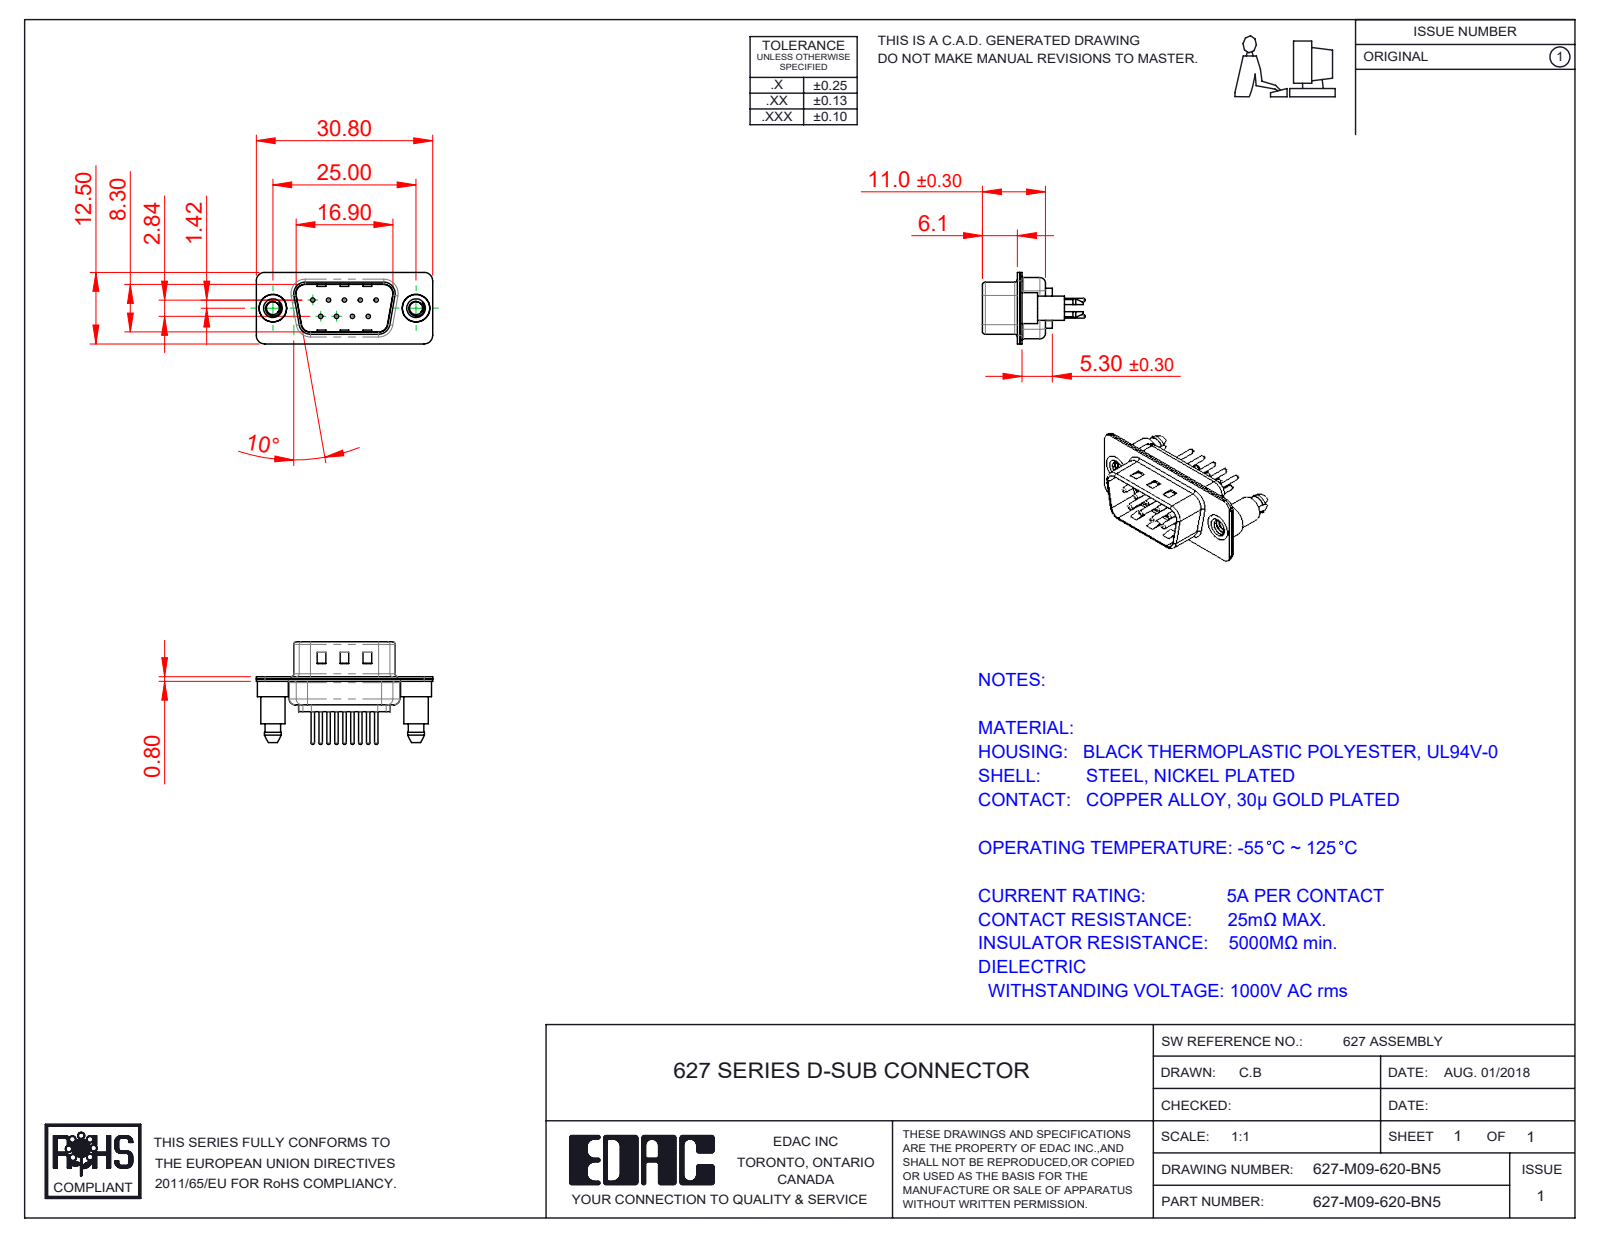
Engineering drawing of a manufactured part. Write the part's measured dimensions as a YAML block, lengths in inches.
part_name: "627M Shell Front_09 Contacts; 627M Housing_09 Contacts; 627-M09-620-BN5; 627M 4-40 Threaded Boardlock (+3 more)"
step_written_by: "SolidWorks 2020 (CONFIG_CONTROL_DESIGN)"
units: inches
bodies: {solids: 14, faces: 687, planar: 186, cylindrical: 287, other: 214}
overall_size: [1.213, 0.705, 0.492]
volume: 0.088
surface_area: 6.056
round_holes:
  - {diameter: 0.03, count: 9}
  - {diameter: 0.063, count: 9}
  - {diameter: 0.079, count: 9}
  - {diameter: 0.089, count: 2}
  - {diameter: 0.157, count: 2}
  - {diameter: 0.189, count: 2}
round_bosses_or_shafts:
  - {diameter: 0.059, count: 9}
  - {diameter: 0.024, count: 9}
  - {diameter: 0.213, count: 2}
  - {diameter: 0.193, count: 2}
  - {diameter: 0.167, count: 2}
partial_cylinders:
  - {radius: 0.059, count: 18}
  - {radius: 0.079, count: 12}
  - {radius: 0.063, count: 10}
  - {radius: 0.02, count: 8}
  - {radius: 0.01, count: 4}
  - {radius: 0.024, count: 4}
  - {radius: 0.026, count: 4}
  - {radius: 0.035, count: 4}
face_to_face_distances: [0.016, 0.031, 0.374, 0.358, 0.343, 0.026, 0.39, 0.047, 0.209, 0.24]
hole_center_spacings: [0.124, 0.109, 0.218, 0.198, 0.198, 0.327, 0.28, 0.294]
